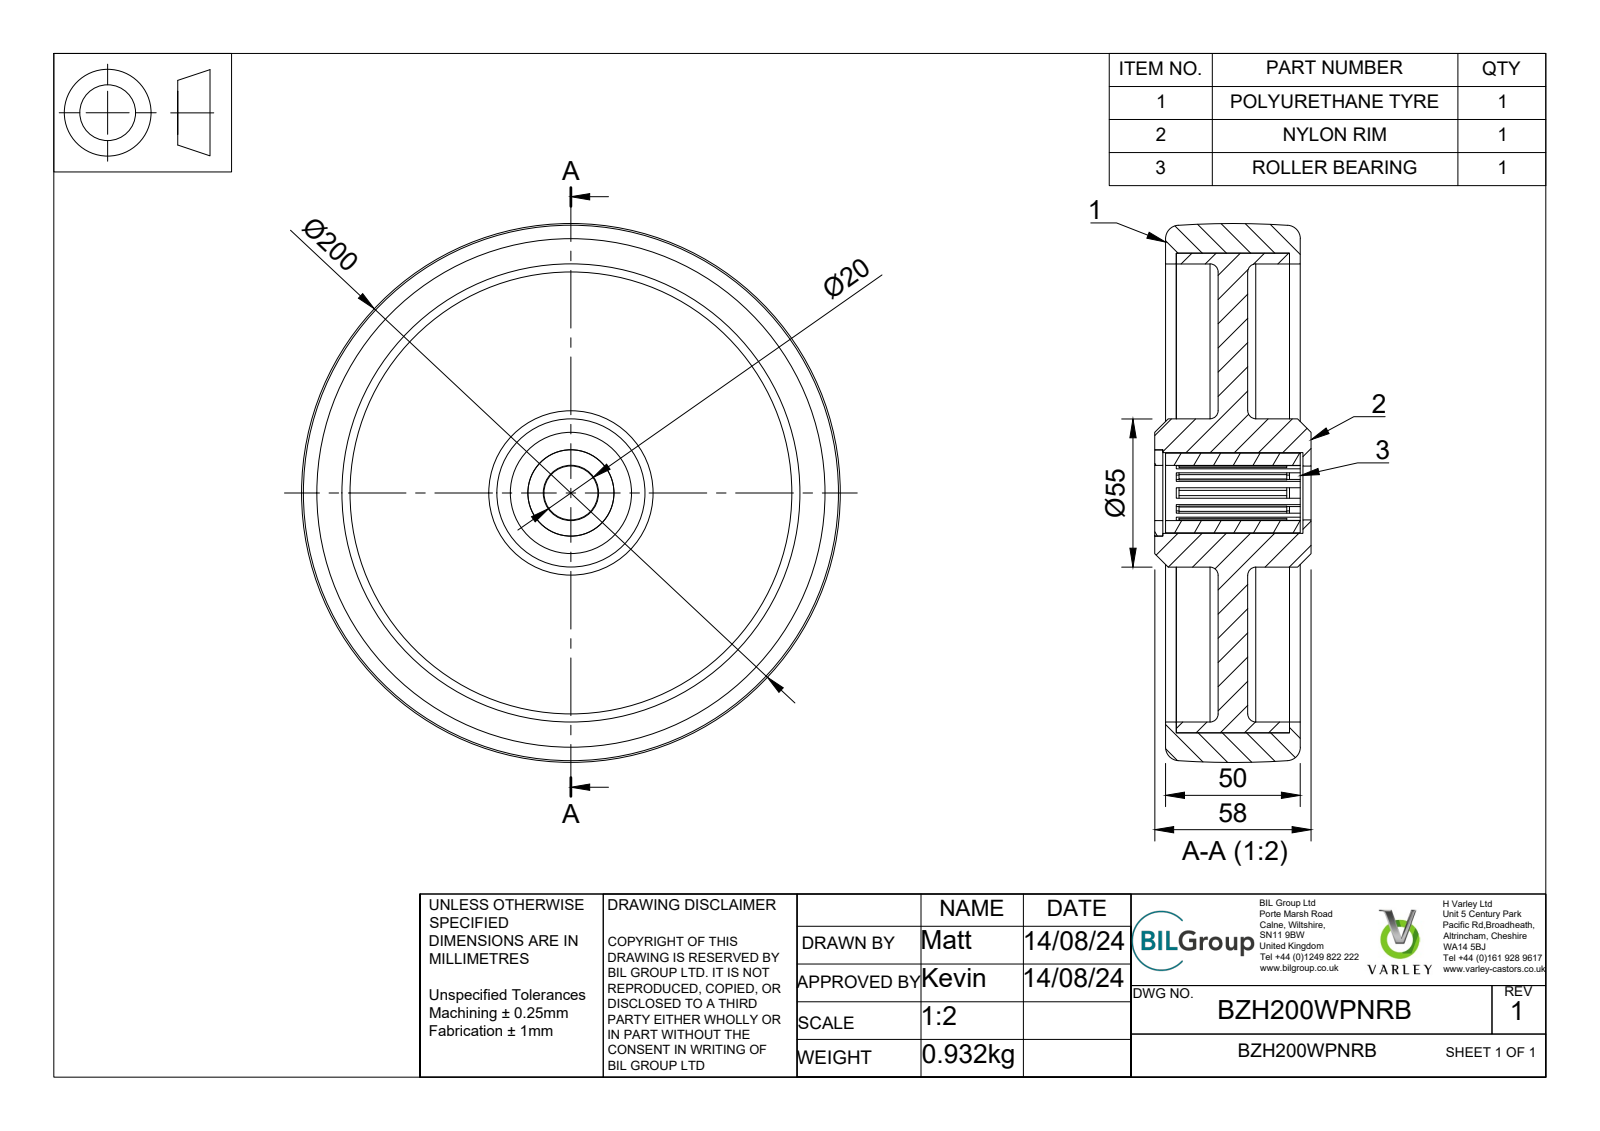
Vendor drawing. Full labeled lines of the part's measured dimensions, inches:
Part name (STEP PRODUCT): BZH200WPNRB v3; NYLON RIM; POLYURETHANE TYRE; RBM20X30X50 v1 (+4 more)
STEP written by: Autodesk Translation Framework v13.14.0.145 (AUTOMOTIVE_DESIGN)
Units: inches
Bodies: 14 solids, 160 faces (96 planar, 55 cylindrical, 9 other)
Overall size (bounding box): 7.874 × 7.874 × 2.283
Volume: 46.14 in³ · Surface area: 301.5 in²
Round holes (diameter × count): ⌀0.787 ×1, ⌀0.807 ×1, ⌀1.181 ×1, ⌀1.26 ×1, ⌀6.693 ×1, ⌀7.008 ×1
Round bosses / shafts (diameter × count): ⌀0.197 ×10, ⌀2.165 ×1, ⌀1.161 ×1
Partial cylindrical surfaces — rounded edges, fillets, slot ends (radius × count): R0.492 ×1
Main face-to-face distances: 0.433, 0.157, 0.768, 1.201, 1.811, 0.61, 1.043, 1.969, 1.654, 0.315
